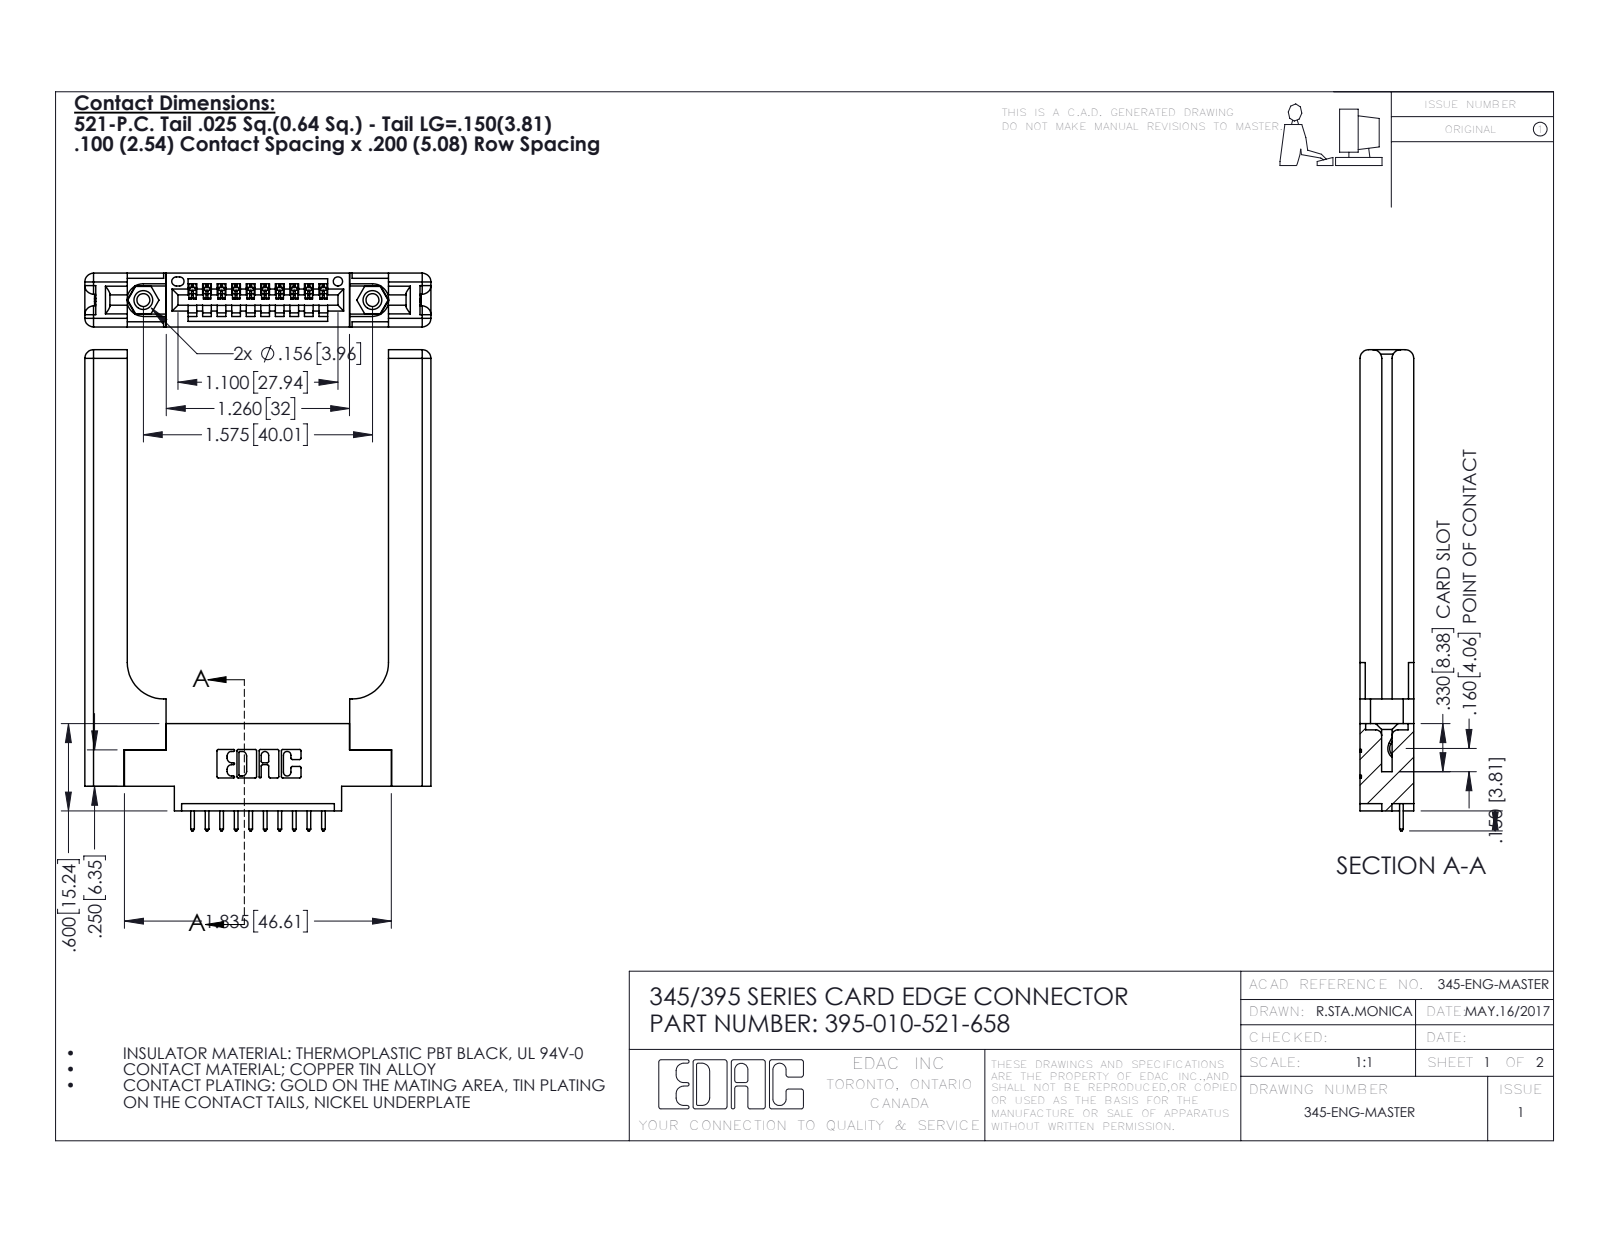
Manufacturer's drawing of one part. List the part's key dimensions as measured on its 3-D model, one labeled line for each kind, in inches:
Part name (STEP PRODUCT): 395-010-521-658; 345 Part_0.170 Offset - 0.156 Dia-TH; 345-220-058_345-220-058; 345-250-001_345-250-001-102 (+1 more)
STEP written by: SolidWorks 2016 (CONFIG_CONTROL_DESIGN)
Units: inches
Bodies: 15 solids, 966 faces (632 planar, 274 cylindrical, 60 other)
Overall size (bounding box): 3.307 × 2.379 × 0.37
Volume: 0.845 in³ · Surface area: 18.56 in²
Round holes (diameter × count): ⌀0.089 ×2, ⌀0.125 ×2, ⌀0.156 ×2, ⌀0.064 ×1
Round bosses / shafts (diameter × count): ⌀0.155 ×2
Partial cylindrical surfaces — rounded edges, fillets, slot ends (radius × count): R0.01 ×22, R0.006 ×20, R0.01 ×20, R0.06 ×16, R0.007 ×6, R0.031 ×6, R0.026 ×3, R0.03 ×2
Main face-to-face distances: 0.37, 0.15, 0.072, 0.22, 0.148, 0.077, 0.298, 1.796, 0.12, 0.071
Hole centre spacings: 0.27, 1.344, 1.575
